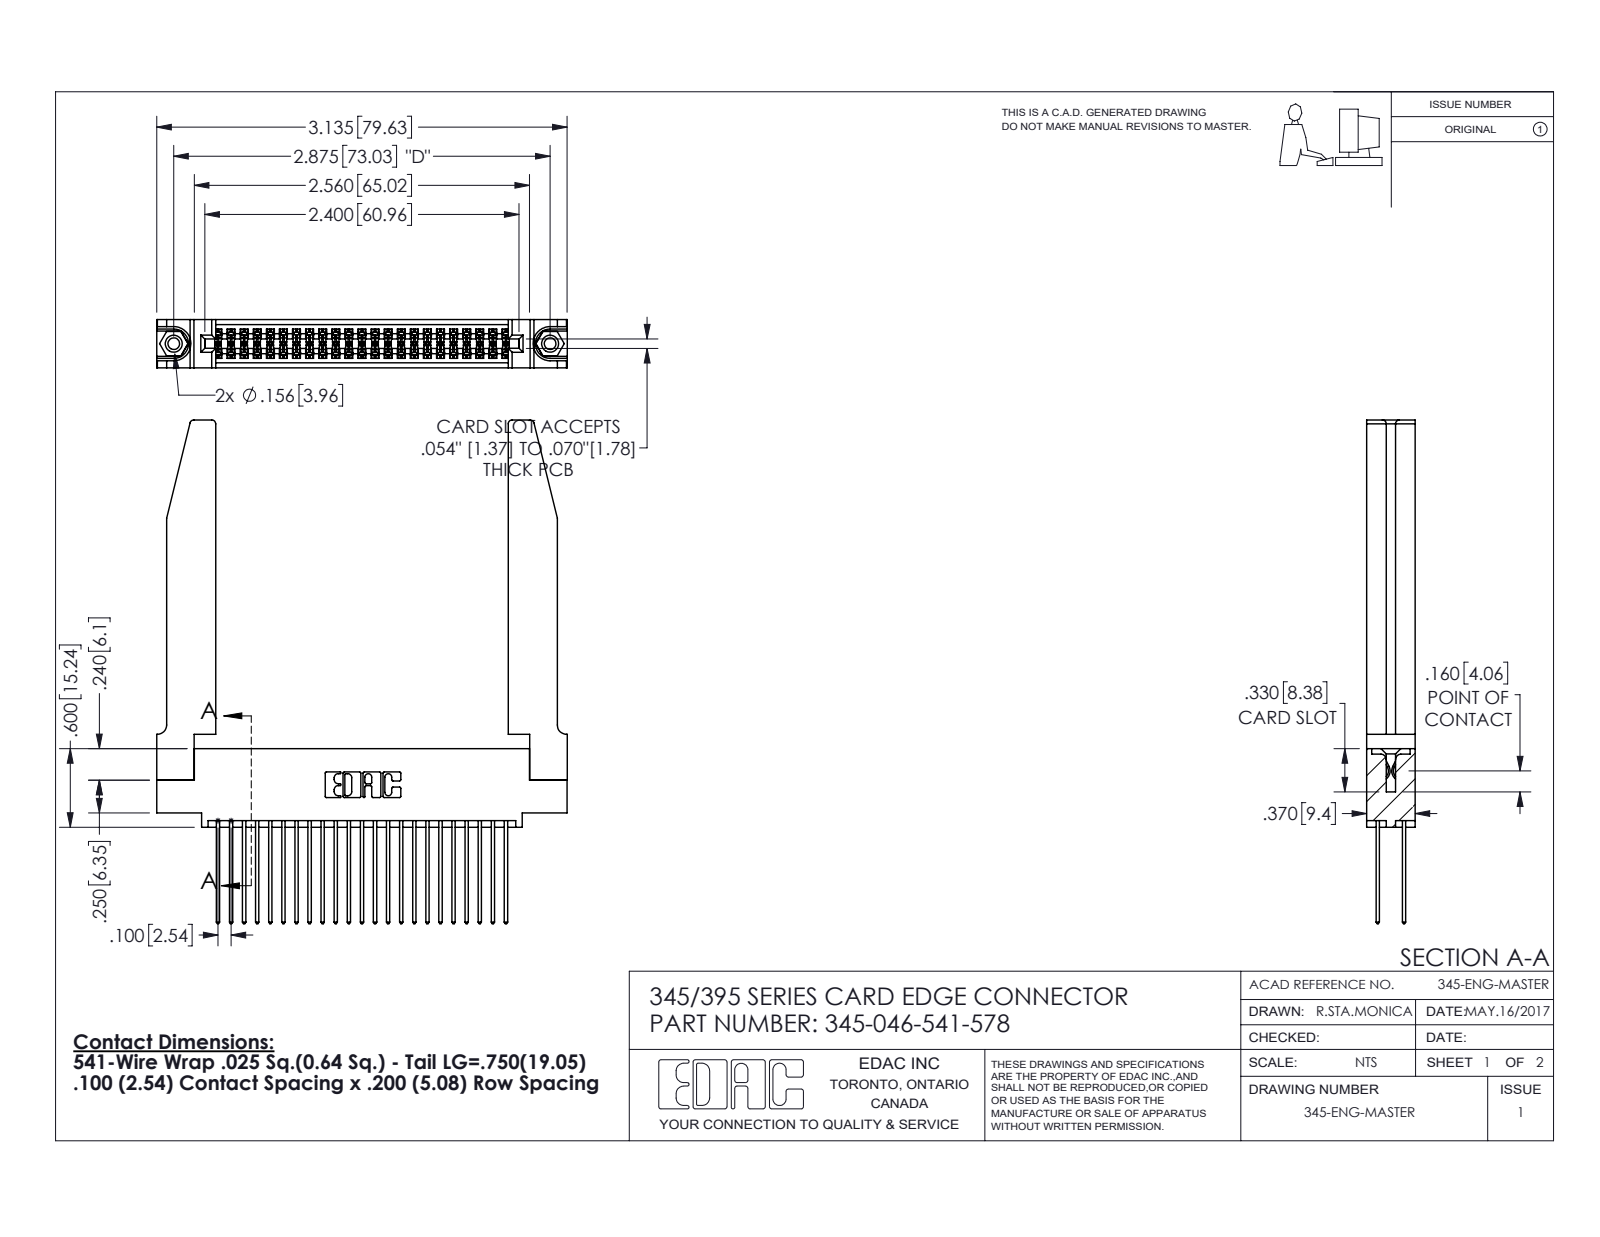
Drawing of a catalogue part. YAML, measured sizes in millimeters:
part_name: "345-250-001_345-250-001-102; 345-292-001_345-293-141; 345-220-078_345-220-078; 345 Part_0.110 Offset - 0.156 Dia-TH (+1 more)"
step_written_by: "SolidWorks 2016 (CONFIG_CONTROL_DESIGN)"
units: millimeters
bodies: {solids: 51, faces: 2664, planar: 1744, cylindrical: 868, other: 52}
overall_size: [97.7, 79.7, 9.4]
volume: 15500
surface_area: 19260
round_holes:
  - {diameter: 2.3, count: 2}
  - {diameter: 3.2, count: 2}
  - {diameter: 4, count: 2}
  - {diameter: 1.6, count: 1}
round_bosses_or_shafts:
  - {diameter: 3.9, count: 2}
partial_cylinders:
  - {radius: 0.2, count: 69}
  - {radius: 0.3, count: 46}
  - {radius: 0.3, count: 22}
  - {radius: 0.8, count: 8}
  - {radius: 0.2, count: 6}
  - {radius: 0.8, count: 6}
  - {radius: 0.7, count: 3}
  - {radius: 0.4, count: 2}
face_to_face_distances: [9.4, 1.8, 7.6, 5.1, 2.5, 6.9, 0.6, 5.7, 4.4, 3.8]
hole_center_spacings: [6.9, 67.1, 73]
